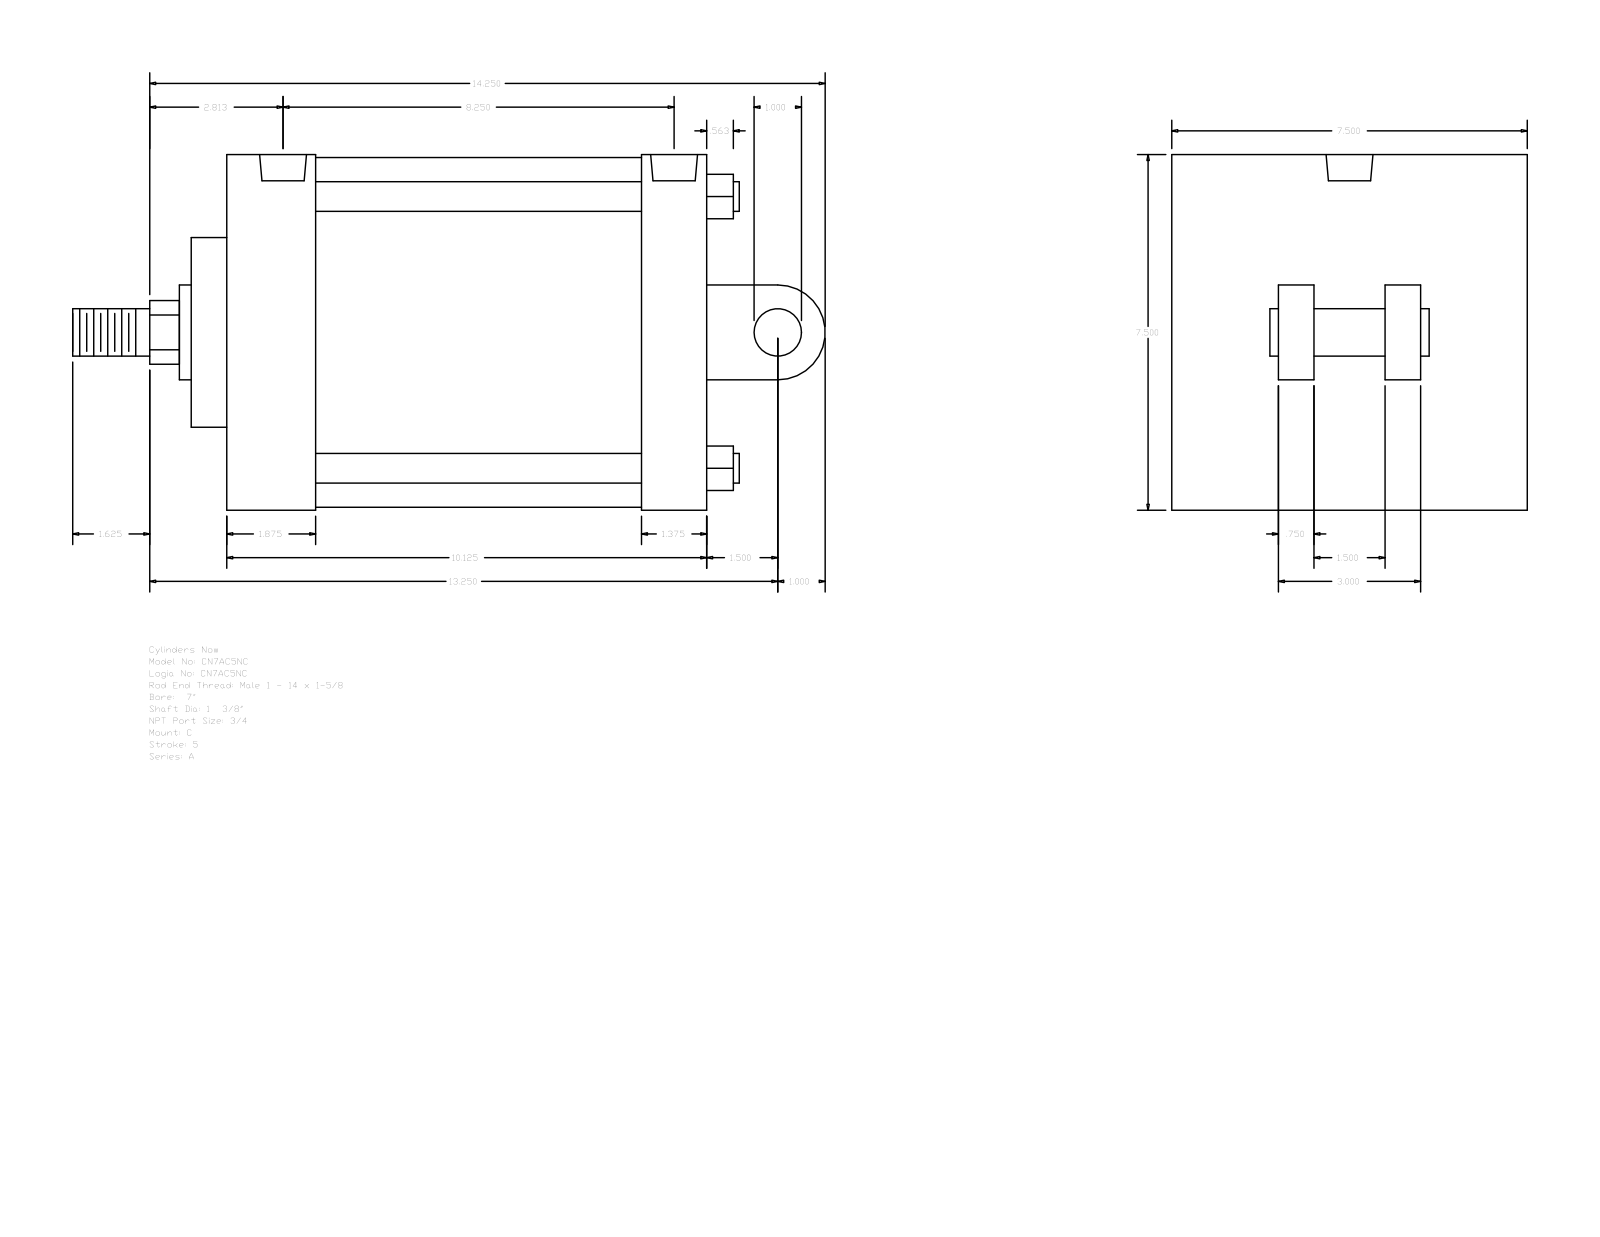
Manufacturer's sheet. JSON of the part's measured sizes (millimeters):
{"part_name": "A_C__0700_1.375", "step_written_by": "GSSL Pune (CONFIG_CONTROL_DESIGN)", "units": "millimeters", "bodies": {"solids": 0, "faces": 104, "planar": 75, "cylindrical": 29, "other": 0}, "overall_size": [403.23, 190.5, 190.5], "round_holes": [[15.08, 4], [25.12, 2]], "round_bosses_or_shafts": [[15.88, 4], [25.4, 2], [187.32, 1], [50.8, 1], [34.92, 1]], "partial_cylinders_radius": [[17.06, 1], [25.4, 1]], "face_to_face_distances": [190.5, 257.18, 76.2, 57.15, 19.04, 276.22, 66.67, 47.63, 209.55, 241.29], "hole_center_spacings": [5.56, 198.43, 203.99, 209.55]}
